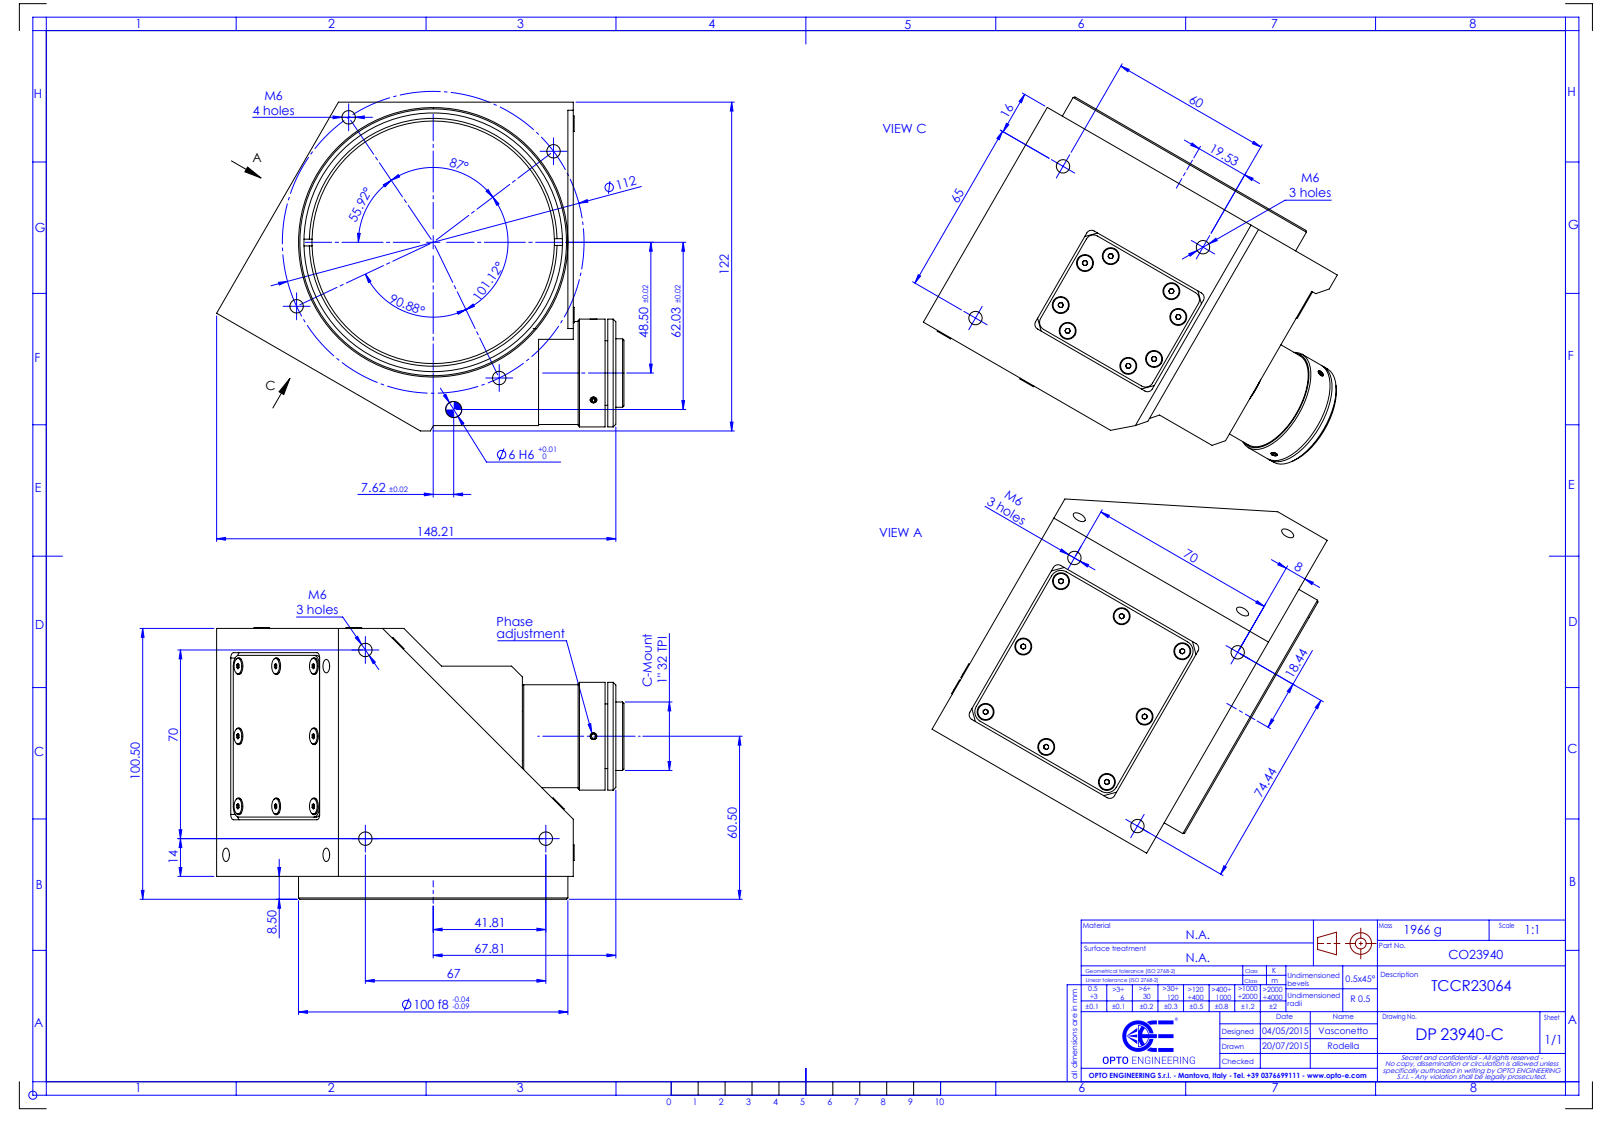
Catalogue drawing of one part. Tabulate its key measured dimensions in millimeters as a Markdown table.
| quantity | value |
| --- | --- |
| part name | DP23940_TCCR23064 |
| STEP written by | SolidWorks 2021 (CONFIG_CONTROL_DESIGN) |
| units | millimeters |
| bodies | 0 solids, 407 faces (189 planar, 110 cylindrical, 108 other) |
| overall size | 151.22 × 122 × 100.83 |
| round holes (diameter × count) | 5 × 13, 6 × 1, 22 × 1, 22.5 × 1, 90 × 1, 96 × 1 |
| round bosses / shafts (diameter × count) | 5.75 × 22, 100 × 1, 40 × 1, 38.2 × 1, 37.8 × 1, 25.4 × 1 |
| partial cylindrical surfaces (radius × count) | 2 × 8, 4 × 6, 3 × 4 |
| main face-to-face distances | 0.5, 92, 120, 1, 2, 36, 18.89, 84, 16.89, 10 |
| hole center spacings | 56, 70, 20.54, 60, 62.5, 65, 67, 69.78 |
